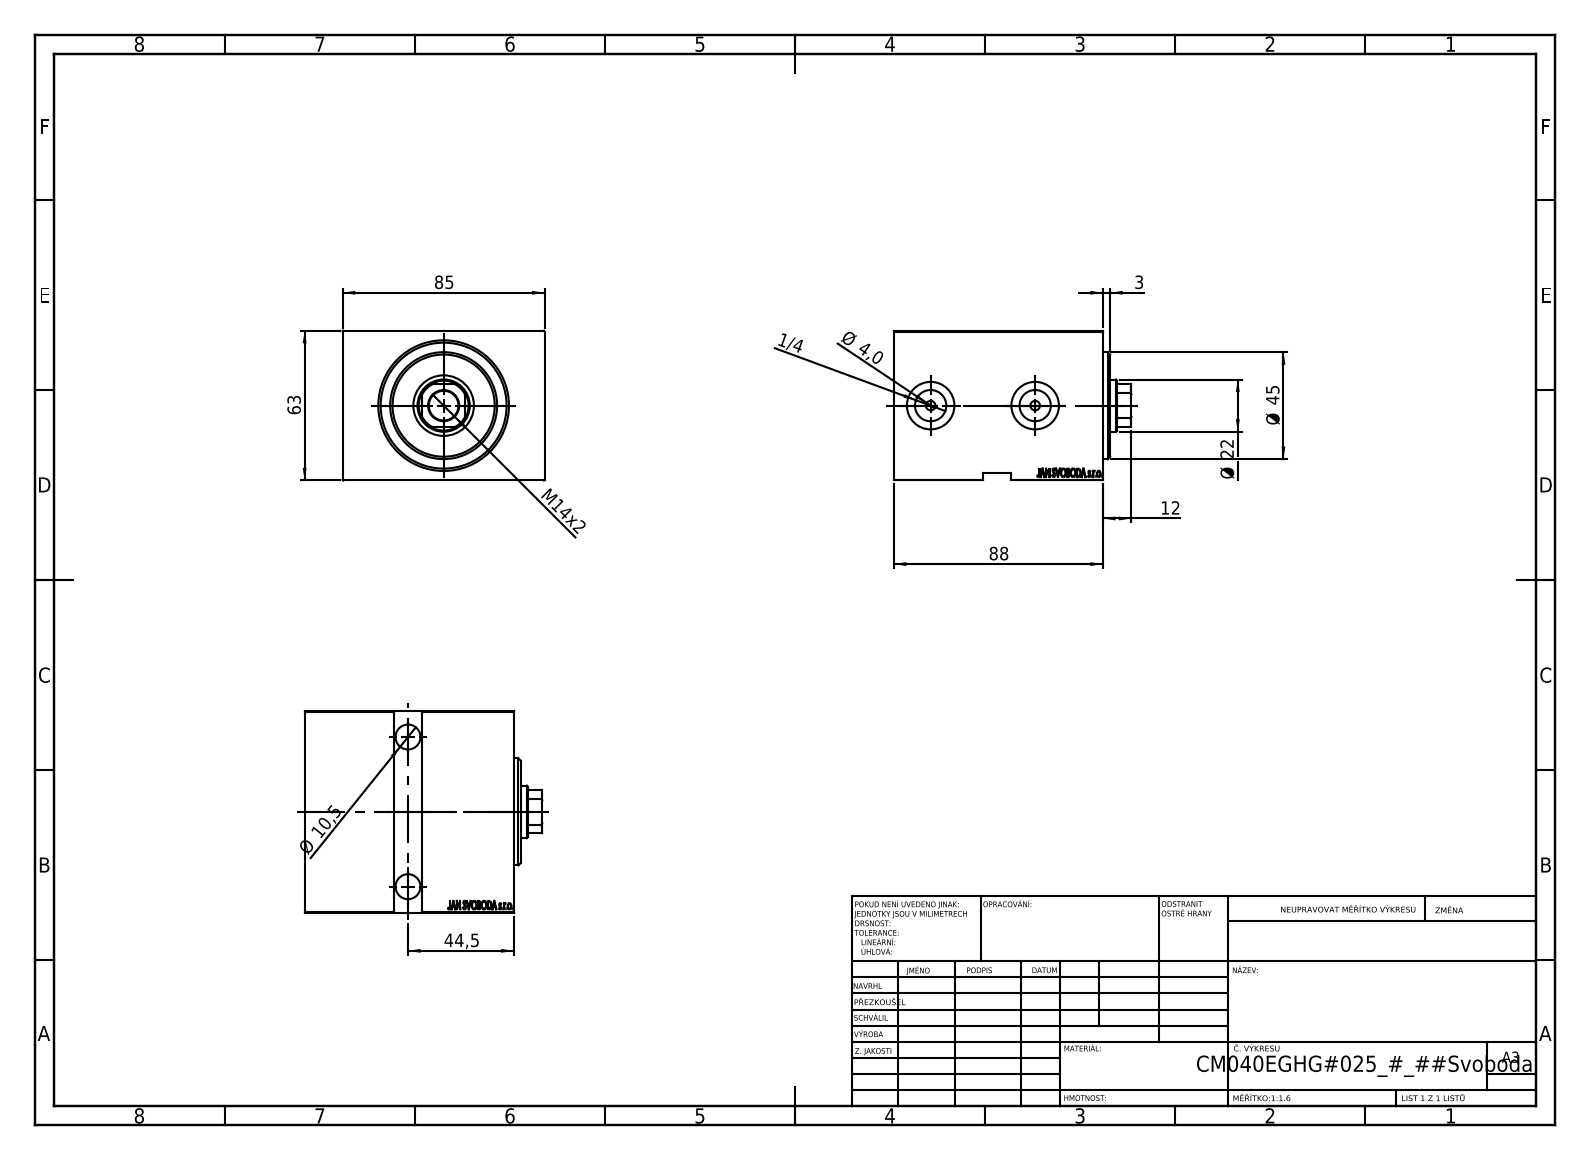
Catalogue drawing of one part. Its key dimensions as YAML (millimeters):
part_name: "V450CM_VC_B; V450CM_E_VCP; V450CM_E_Body"
step_written_by: "SolidWorks 2019 (CONFIG_CONTROL_DESIGN)"
units: millimeters
bodies: {solids: 3, faces: 846, planar: 408, cylindrical: 44, other: 394}
overall_size: [100, 85, 63]
volume: 438050
surface_area: 71707
round_holes:
  - {diameter: 4, count: 2}
  - {diameter: 10.5, count: 2}
  - {diameter: 13.16, count: 2}
  - {diameter: 16.5, count: 2}
  - {diameter: 20, count: 2}
  - {diameter: 12.5, count: 1}
  - {diameter: 22, count: 1}
  - {diameter: 25.5, count: 1}
  - {diameter: 40, count: 1}
  - {diameter: 53, count: 1}
round_bosses_or_shafts:
  - {diameter: 45, count: 1}
  - {diameter: 42, count: 1}
partial_cylinders:
  - {radius: 10.5, count: 1}
face_to_face_distances: [63, 85, 88, 12, 76, 3, 5, 83, 71, 40]
hole_center_spacings: [44, 63]
